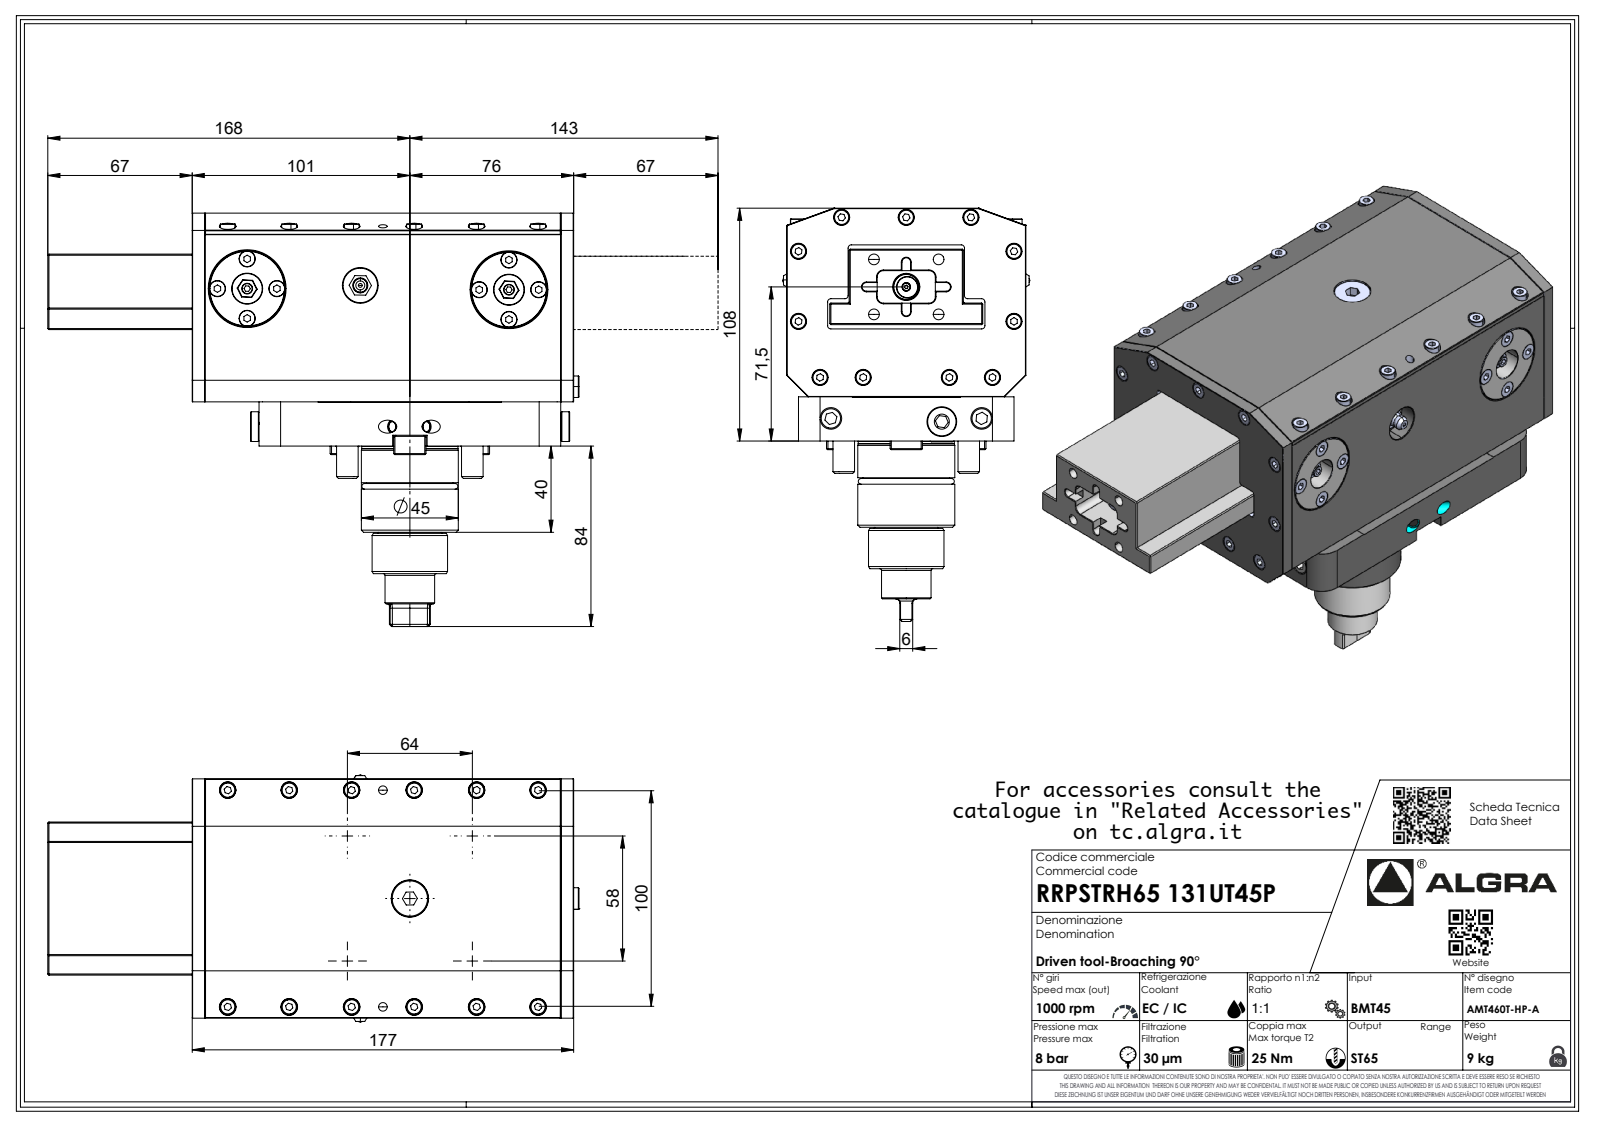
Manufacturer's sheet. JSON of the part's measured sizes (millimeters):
{"part_name": "RRPSTRH65131UT45P", "step_written_by": "SolidWorks 2023 (AUTOMOTIVE_DESIGN)", "units": "millimeters", "bodies": {"solids": 1, "faces": 770, "planar": 512, "cylindrical": 114, "other": 144}, "overall_size": [246.47, 191.7, 114.6], "volume_mm3": 2179000, "surface_area_mm2": 140546, "round_holes": [[2.1, 1], [61, 1]], "round_bosses_or_shafts": [[55, 1], [45, 1], [44.6, 1], [40.2, 1], [35, 1], [23, 1], [10, 1], [6.37, 1]], "partial_cylinders_radius": [[2.5, 12], [3.5, 12], [0.33, 7], [0.52, 7], [3.7, 7], [2, 6], [9.5, 5], [3, 4]], "face_to_face_distances": [111, 87.5, 20.5, 108, 54, 20.3, 87.7, 177, 5.5, 105.5]}
